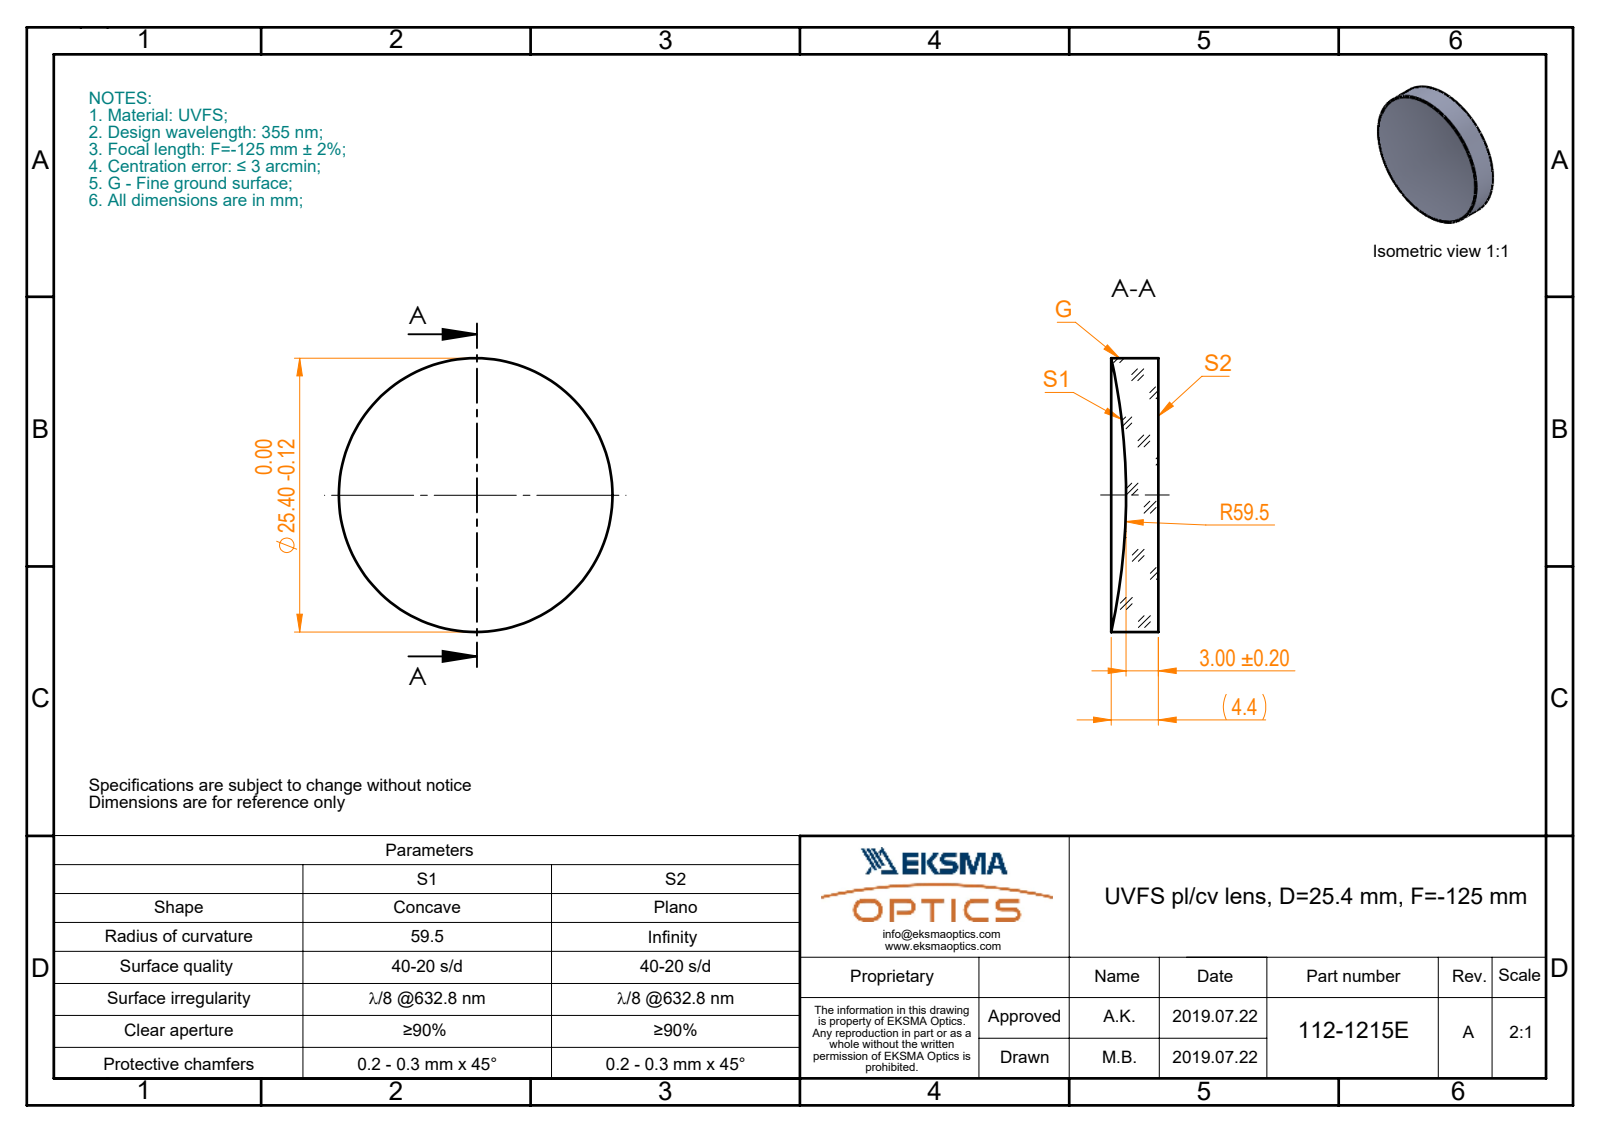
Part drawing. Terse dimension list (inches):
name: 112-1215E UVFS pl-cv 25.4 F-125
written by: SolidWorks 2017 (CONFIG_CONTROL_DESIGN)
unit: in
bodies: 1 solid, 5 faces (1 planar, 2 cylindrical, 2 other)
size: 1 × 1 × 0.172
volume: 0.114 in³; area: 2.12 in²
bosses: 1× ⌀1
